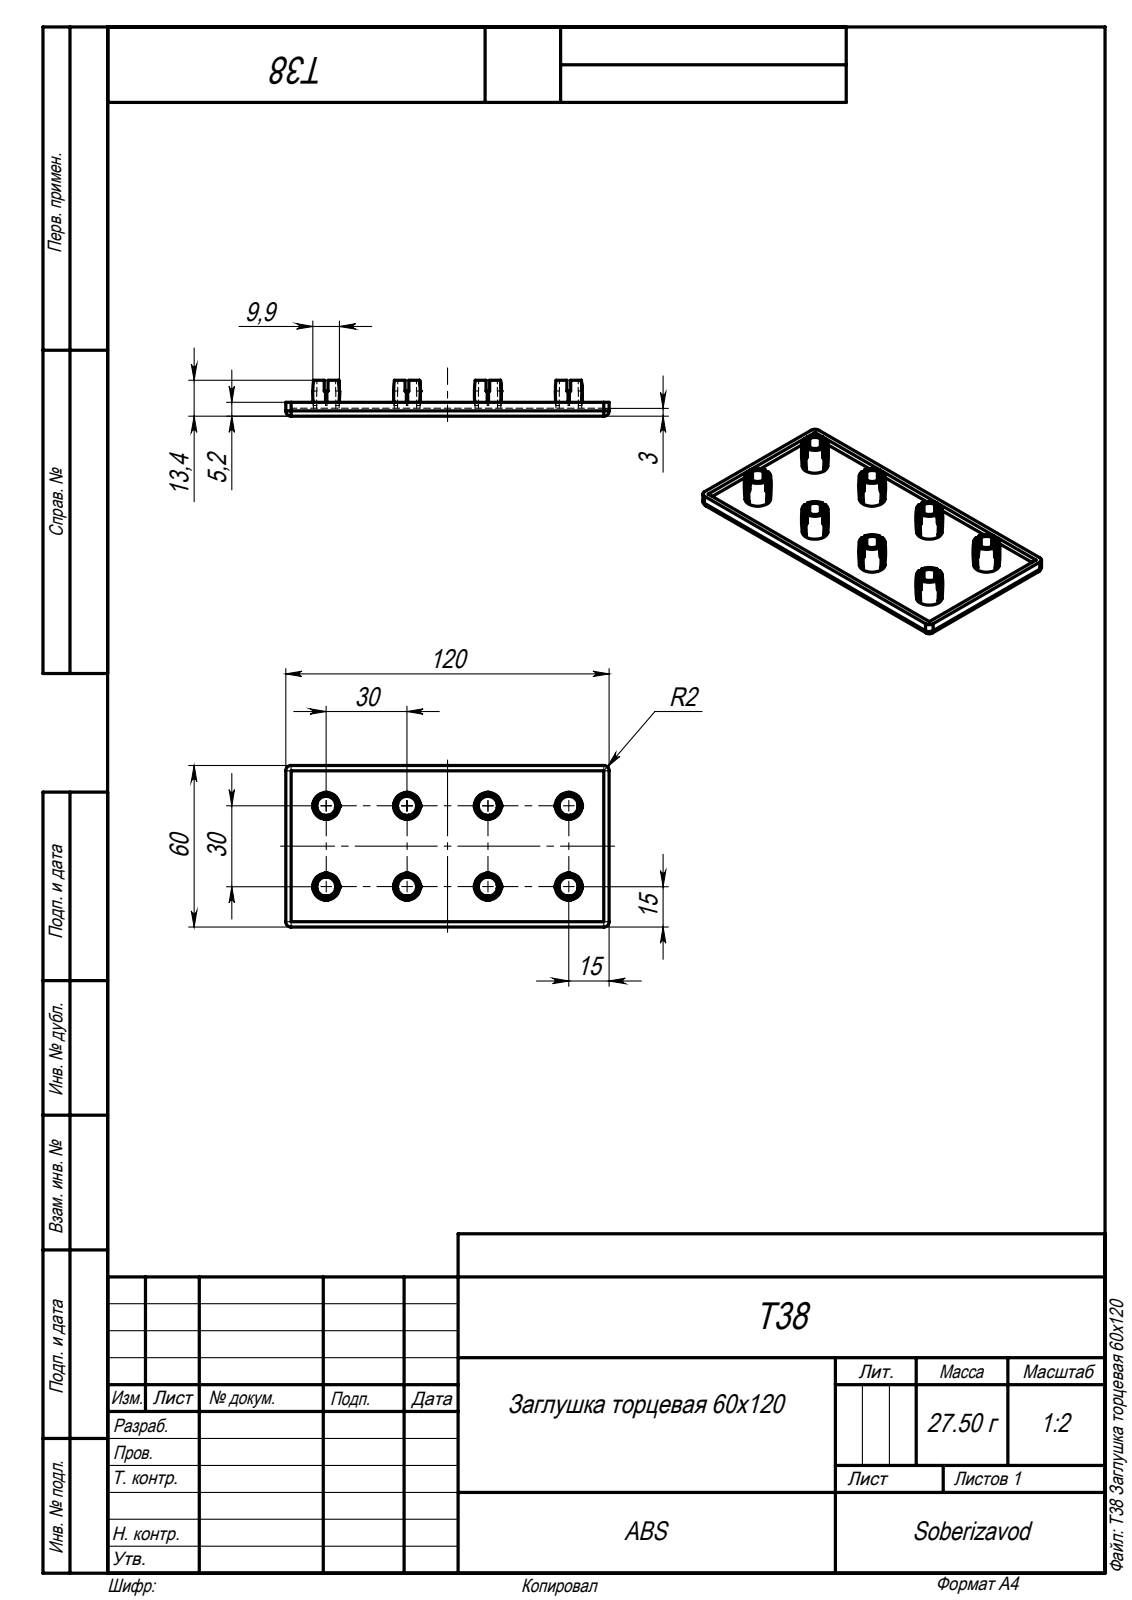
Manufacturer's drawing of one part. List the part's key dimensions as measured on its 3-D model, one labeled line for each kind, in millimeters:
Part name (STEP PRODUCT): T38 Заглушка торцевая 60х120
STEP written by: SolidWorks 2018 (AUTOMOTIVE_DESIGN)
Units: millimetres
Bodies: 1 solid, 319 faces (275 planar, 24 cylindrical, 20 other)
Overall size (bounding box): 120 × 60 × 13.35
Volume: 25 121 mm³ · Surface area: 21 417 mm²
Round holes (diameter × count): ⌀7.1 ×8
Partial cylindrical surfaces — rounded edges, fillets, slot ends (radius × count): R2 ×8
Main face-to-face distances: 2.95, 2, 5.15, 2.2, 60, 30, 58, 0.45, 0.95, 56
Hole centre spacings: 30, 42.43, 60, 67.08, 90, 94.87
